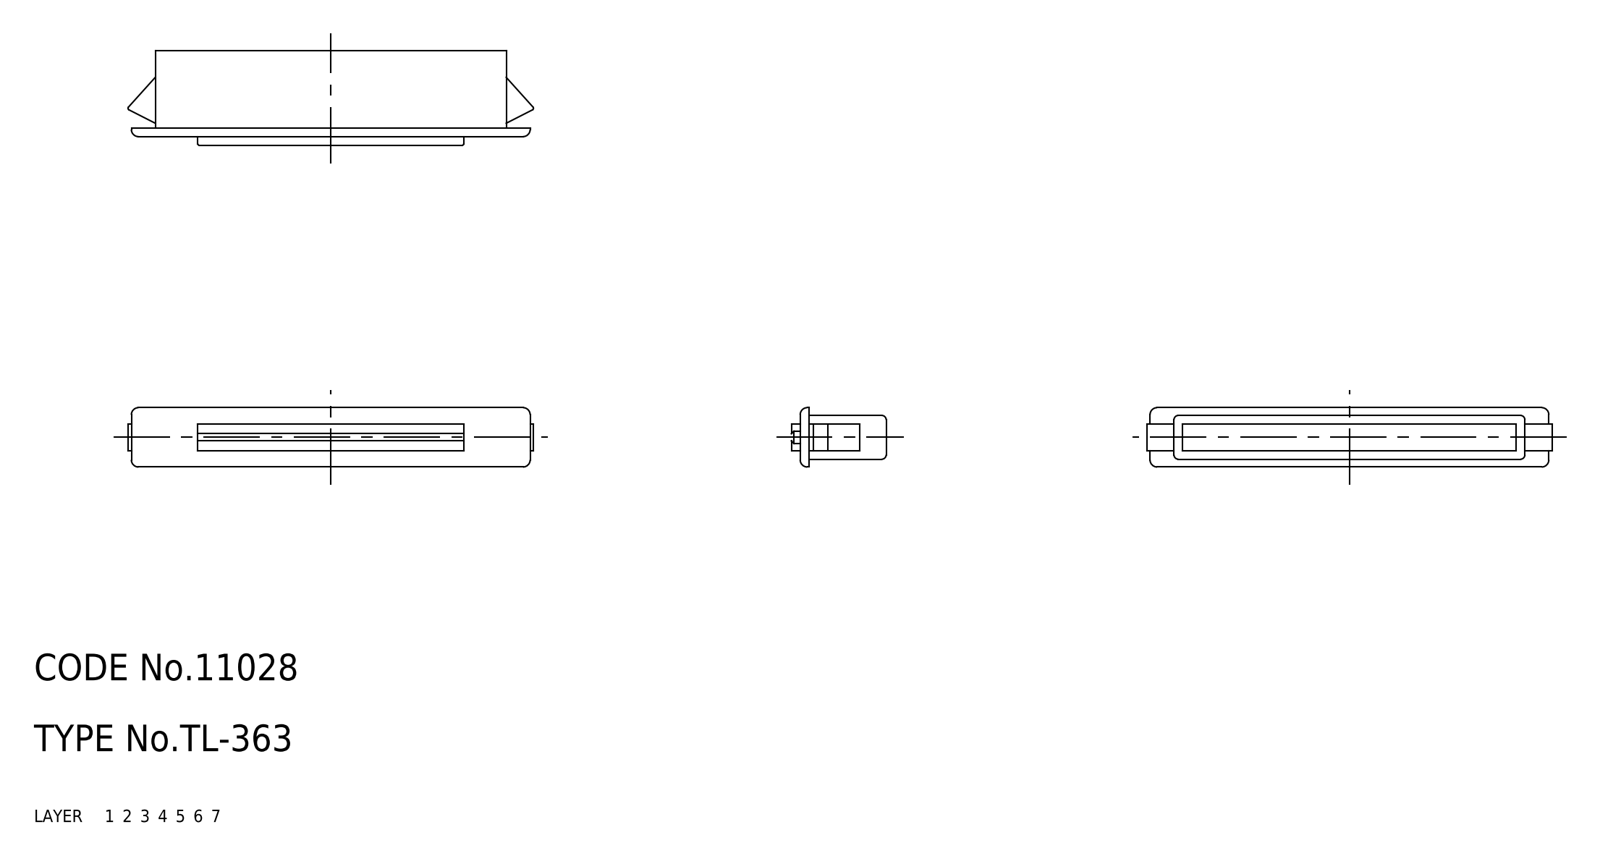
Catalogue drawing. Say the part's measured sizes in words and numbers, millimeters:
The part is named "67111378; 67111391; 67111404". Its 3-D file was written by "CADfix (AUTOMOTIVE_DESIGN)". It is 3 solids with 80 faces: 0 planar, 0 cylindrical and 80 other. Overall it measures 45.75 by 10.7 by 6.7 millimeters. Its volume is 2 047 cubic millimeters and its surface area 3 510 square millimeters.
